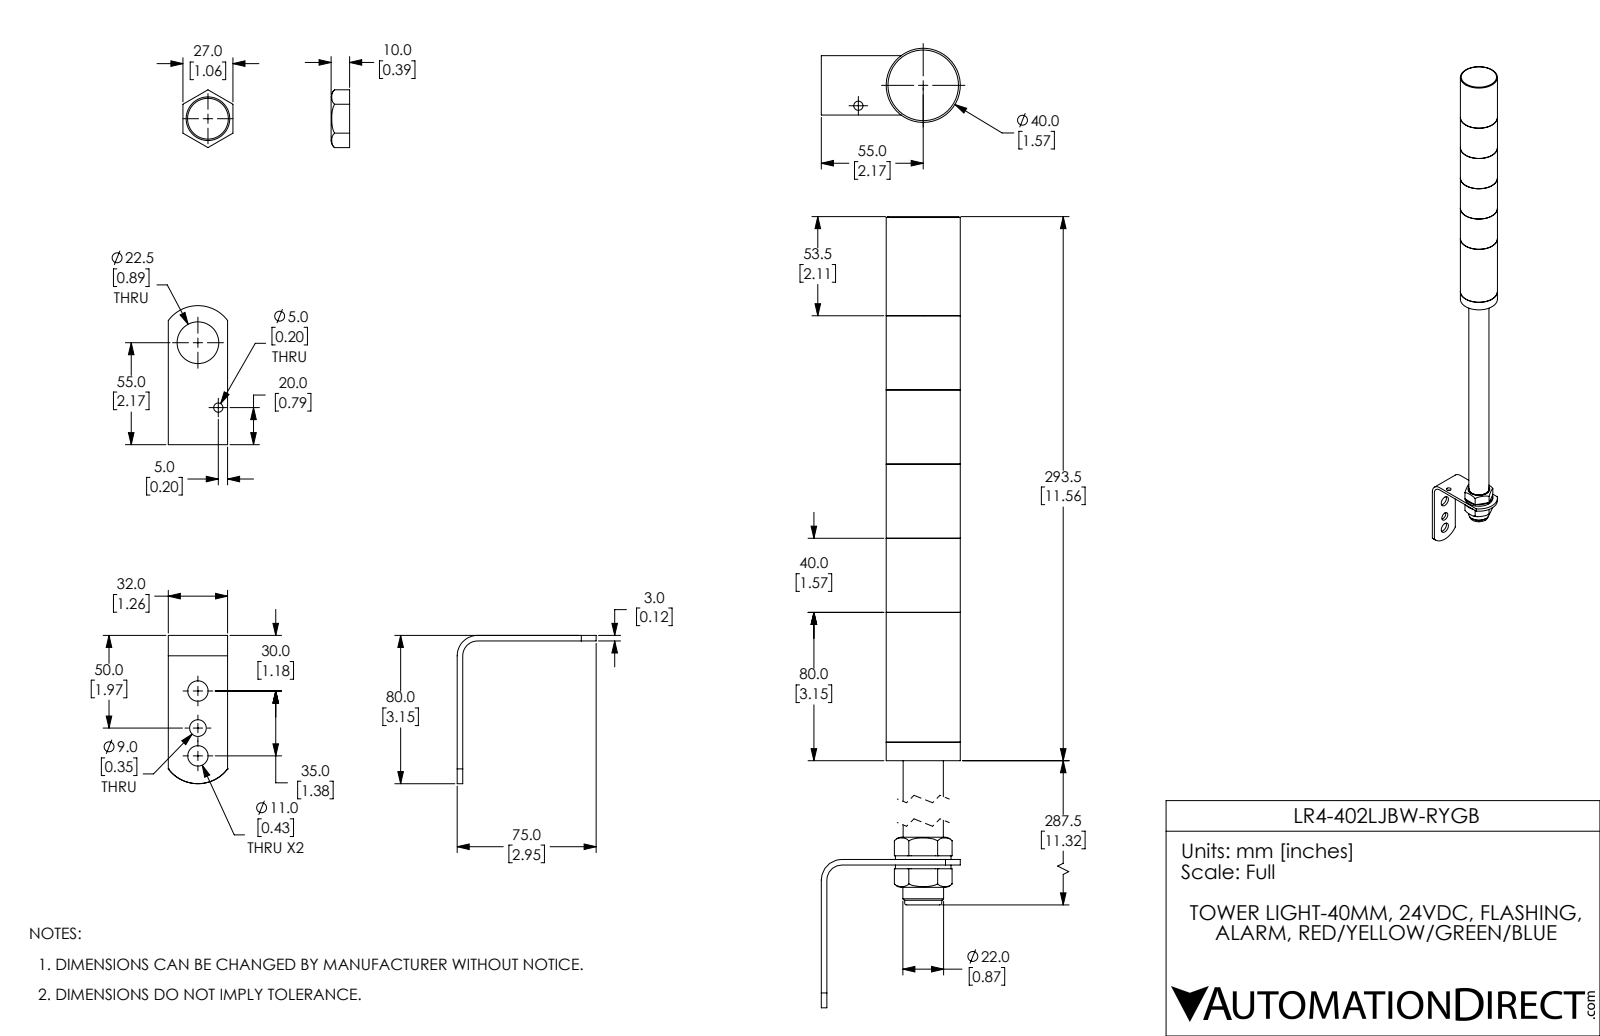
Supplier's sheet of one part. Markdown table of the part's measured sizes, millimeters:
| quantity | value |
| --- | --- |
| part name | LR4-402LJBW-RYGB |
| STEP written by | SolidWorks 2017 (AUTOMOTIVE_DESIGN) |
| units | millimeters |
| bodies | 13 solids, 175 faces (64 planar, 97 cylindrical, 14 other) |
| overall size | 636.5 × 75 × 40 |
| volume | 433 400 mm³ |
| surface area | 126 600 mm² |
| round holes (diameter × count) | 3.2 × 2, 11 × 2, 5 × 1, 7.7 × 1, 9 × 1, 17.7 × 1, 22 × 1, 22.5 × 1, 27.6 × 1, 35.2 × 1, 35.3 × 1, 37.2 × 1 |
| round bosses / shafts (diameter × count) | 40 × 1, 37.1 × 1, 34.7 × 1, 30 × 1, 21.7 × 1 |
| partial cylindrical surfaces (radius × count) | 20 × 1 |
| main face-to-face distances | 40, 80, 120, 90.3, 80.3, 120.3, 160.3, 130.3, 10.3, 50.3 |
| hole center spacings | 7.2, 14.4, 15, 20, 29.9, 35, 36.7, 43.6 |
